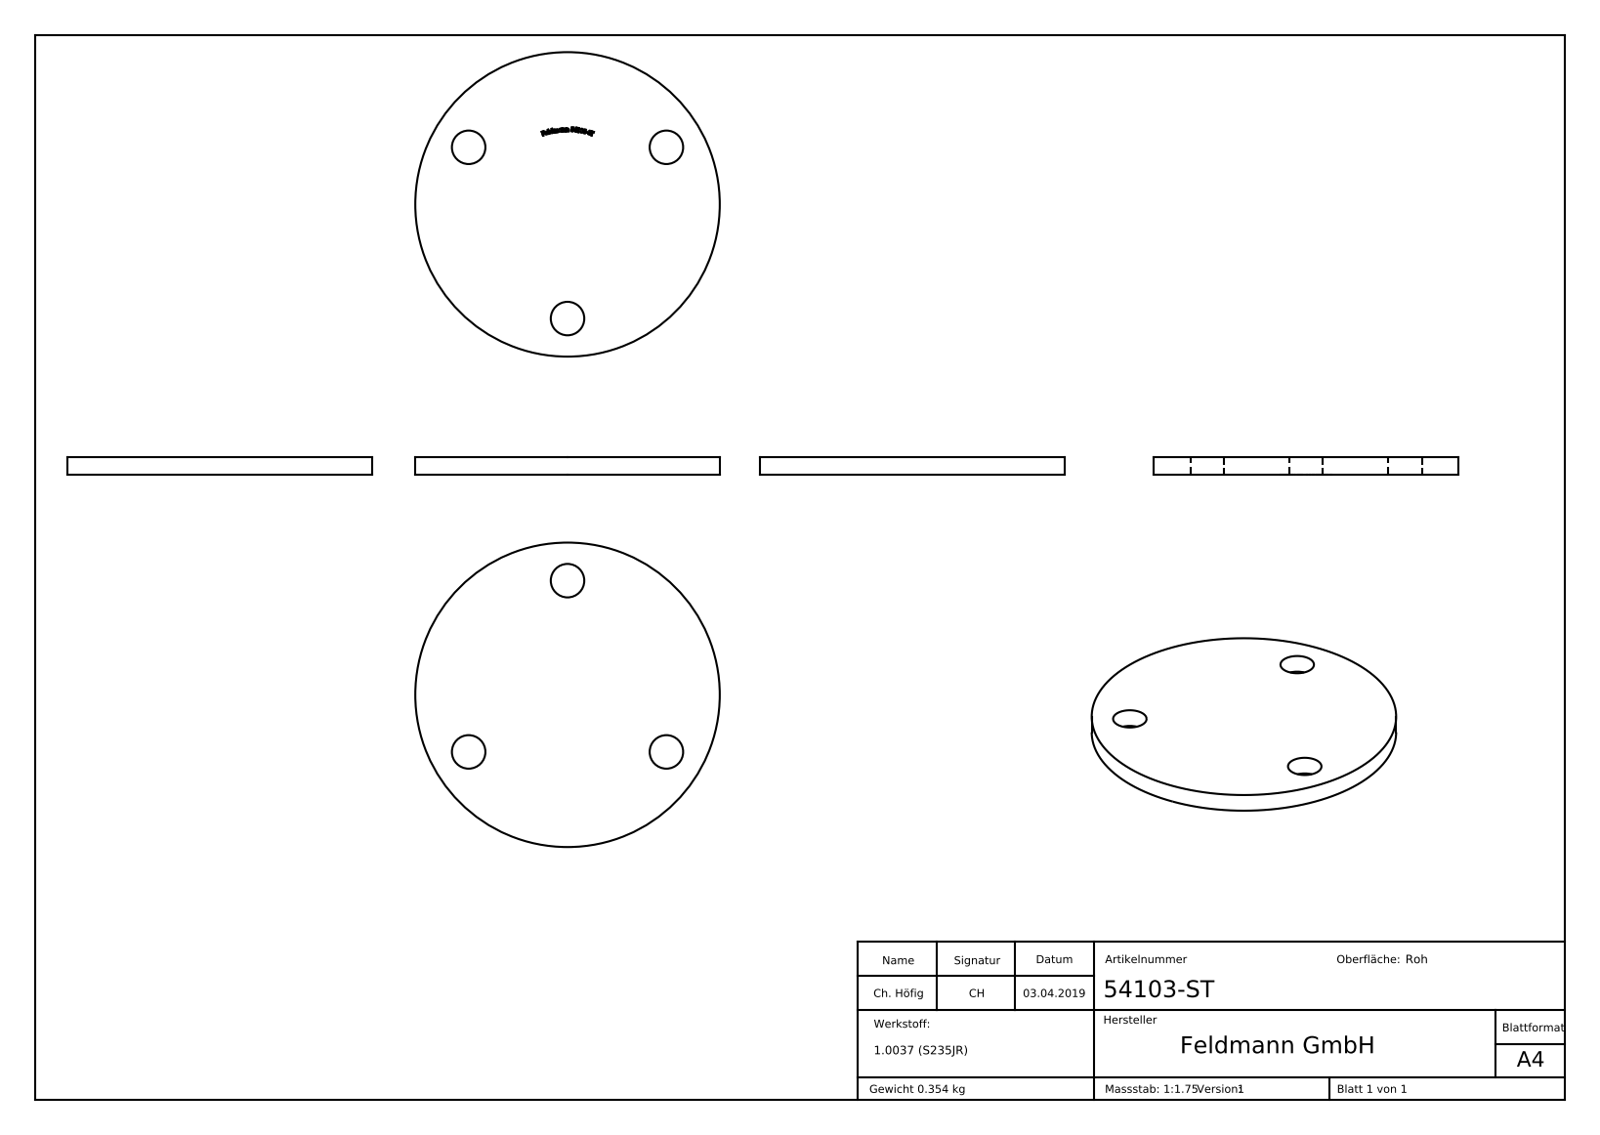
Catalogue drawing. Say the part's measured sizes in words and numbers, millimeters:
The part is named "54103-ST". Its 3-D file was written by "SolidWorks 2015 (CONFIG_CONTROL_DESIGN)". It is 1 solid with 221 faces: 119 planar, 8 cylindrical and 94 other. Overall it measures 100 by 100 by 6 millimeters. Its volume is 45 413 cubic millimeters and its surface area 17 653 square millimeters. Round holes: 3 of diameter 11. Round bosses or shafts: 1 of diameter 100. The main face-to-face distances are 6, 5.9, 0.54, 0.85, 1.33, 0.73, 0.72, 0.6, 1.46, 0.67. The hole center spacings are 64.95, 64.96.
